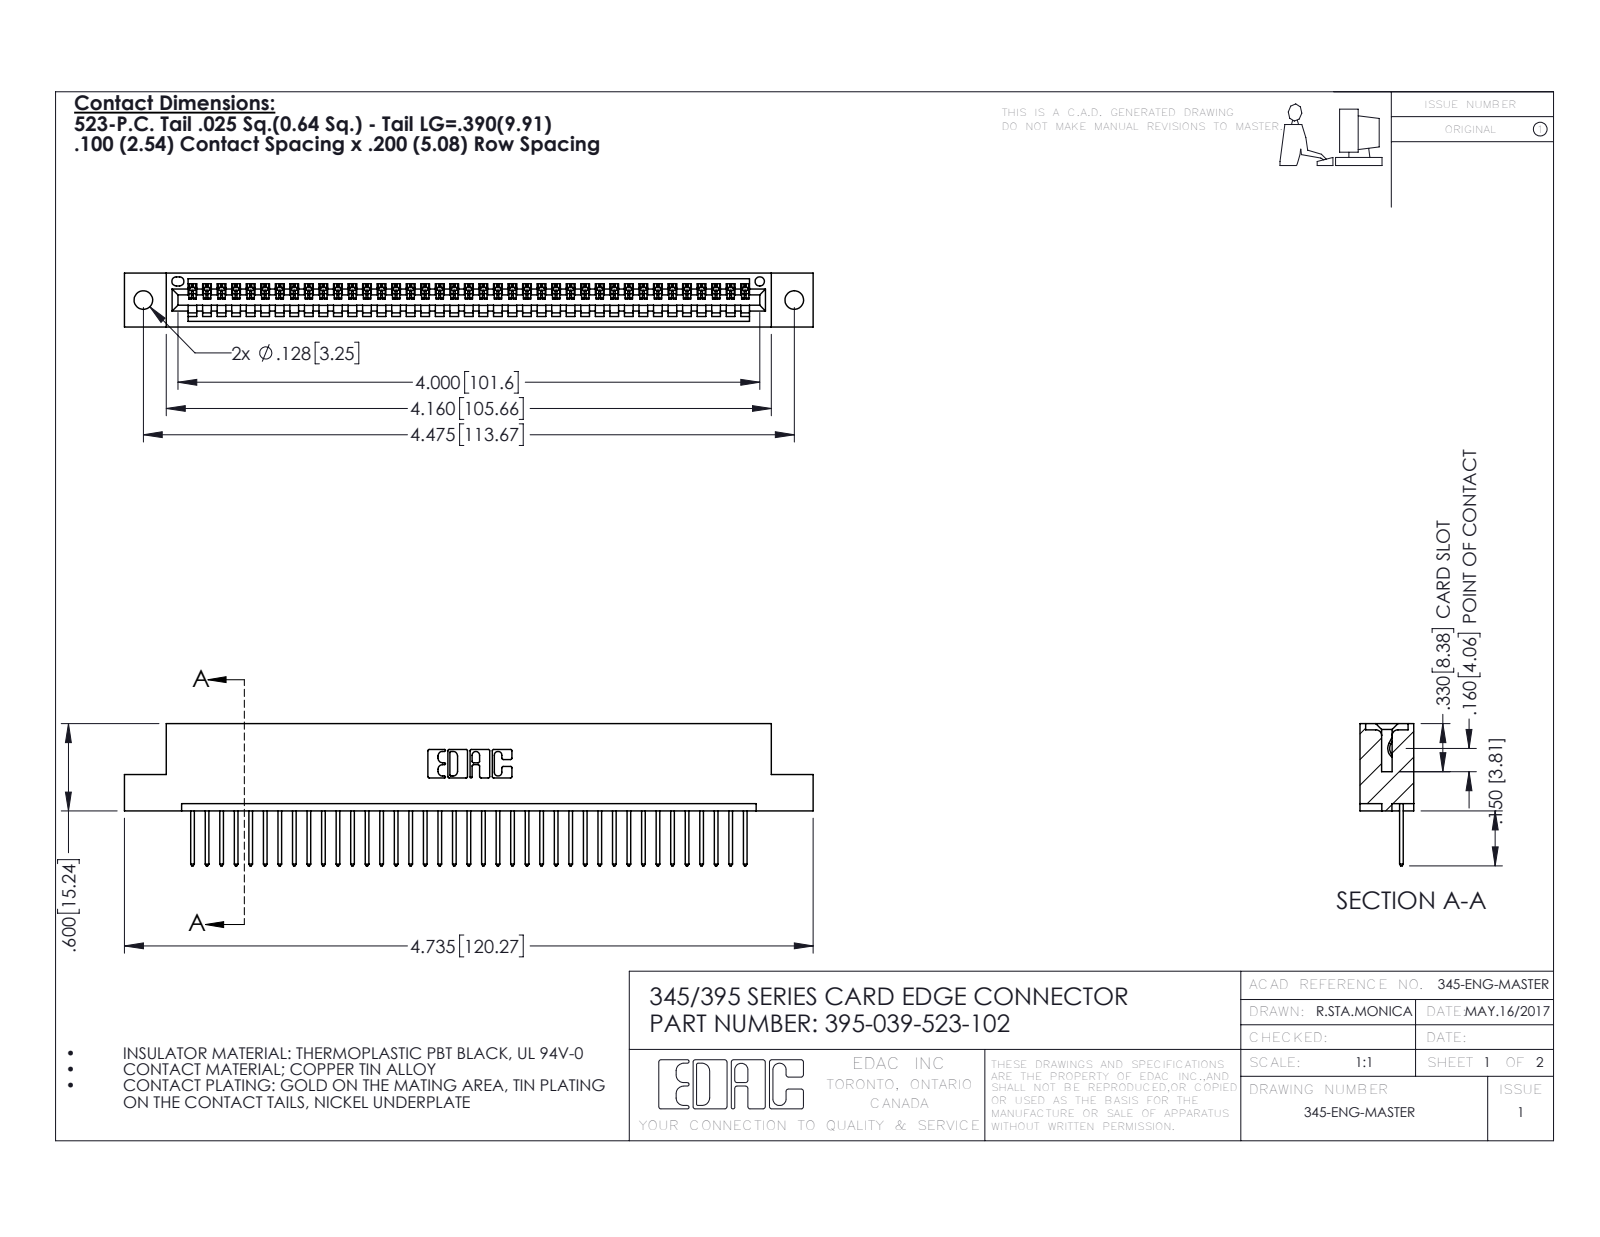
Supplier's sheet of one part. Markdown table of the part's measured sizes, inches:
| quantity | value |
| --- | --- |
| part name | 395-039-523-102; 345 Part_Flush Mounting Lugs - 0.128 Dia; 345-292-001_345-293-123 |
| STEP written by | SolidWorks 2016 (CONFIG_CONTROL_DESIGN) |
| units | inches |
| bodies | 40 solids, 2388 faces (1640 planar, 748 cylindrical, 0 other) |
| overall size | 4.735 × 0.977 × 0.37 |
| volume | 0.692 in³ |
| surface area | 22.95 in² |
| round holes (diameter × count) | 0.128 × 2, 0.064 × 1 |
| partial cylindrical surfaces (radius × count) | 0.006 × 78, 0.01 × 78, 0.01 × 22, 0.007 × 6, 0.031 × 6, 0.026 × 3, 0.031 × 2, 0.04 × 2 |
| main face-to-face distances | 0.298, 0.072, 0.37, 0.2, 0.098, 0.272, 0.025, 0.225, 0.149, 0.072 |
| hole center spacings | 0.27, 4.239, 4.475 |
